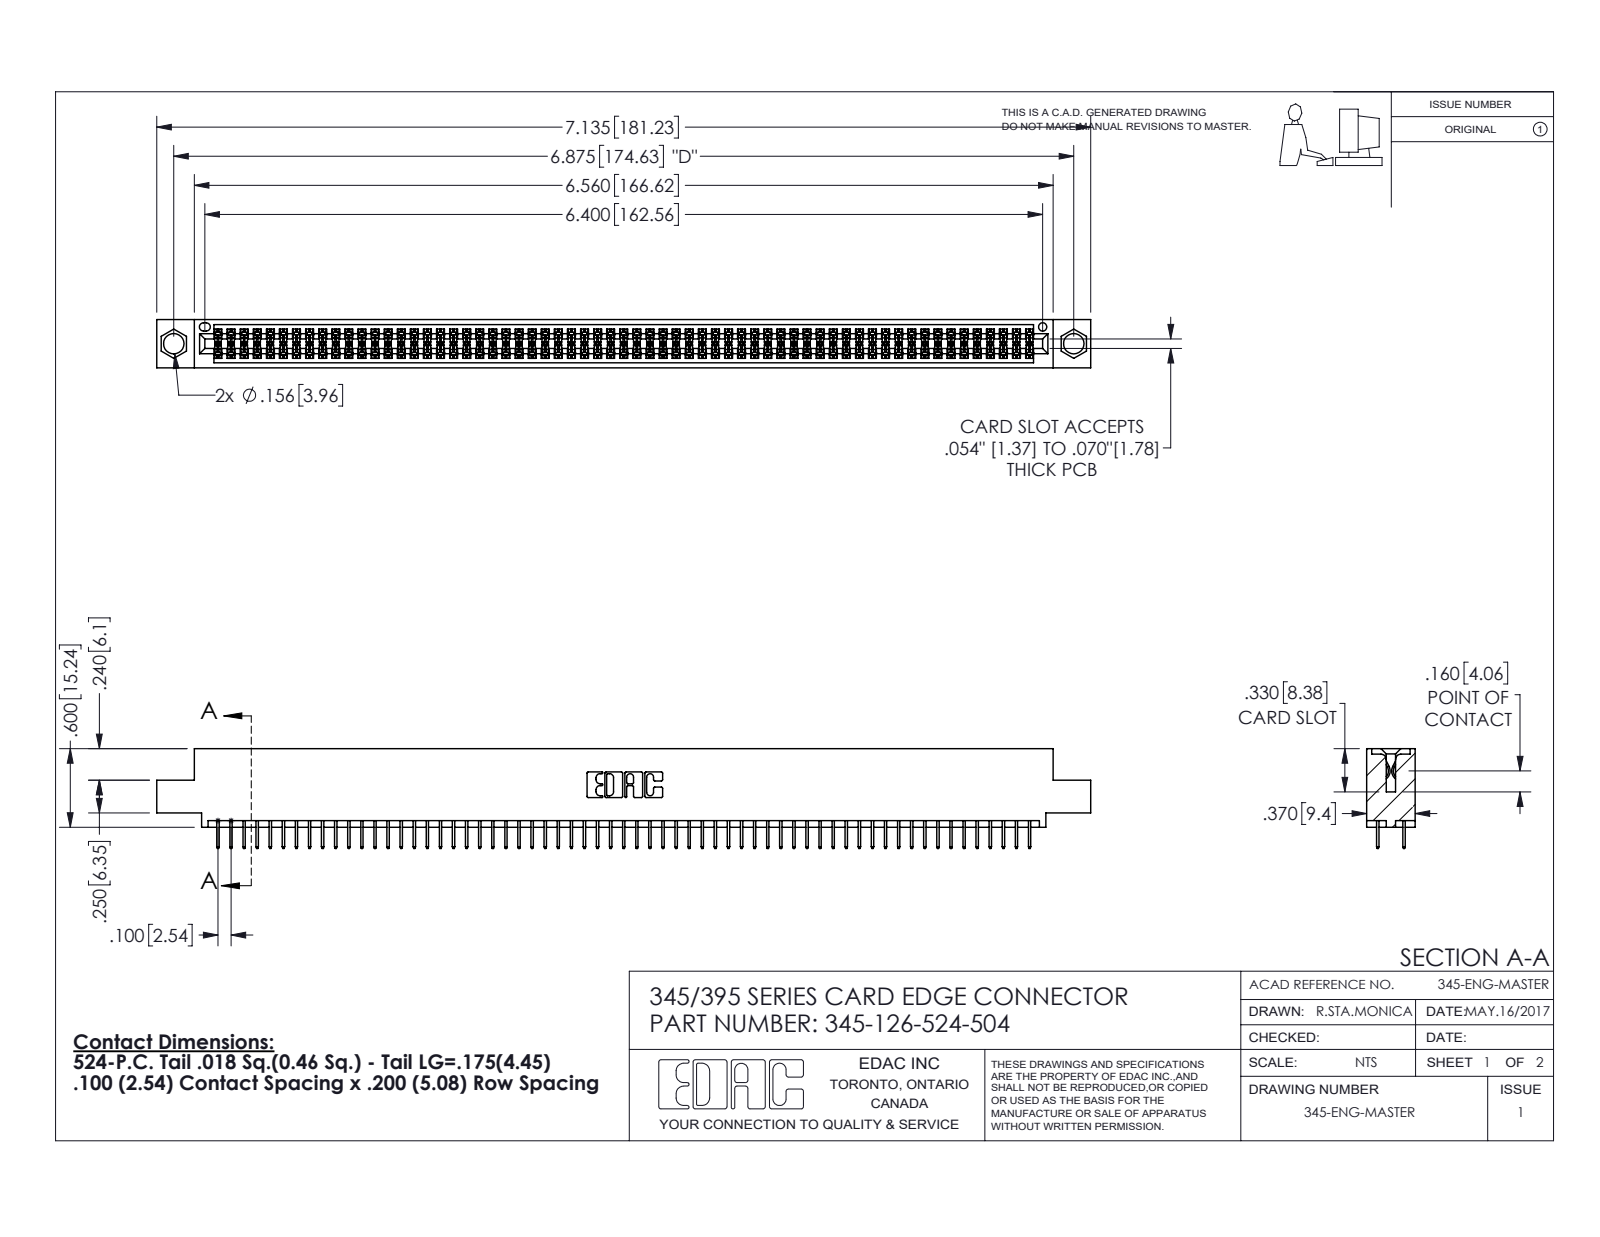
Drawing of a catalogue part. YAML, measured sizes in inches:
part_name: "345-292-001_345-293-124; 345 Part_0.110 Offset - 0.156 Dia-TI; 345-126-524-504"
step_written_by: "SolidWorks 2020 (CONFIG_CONTROL_DESIGN)"
units: inches
bodies: {solids: 127, faces: 6948, planar: 5012, cylindrical: 1936, other: 0}
overall_size: [7.135, 0.762, 0.37]
volume: 1.064
surface_area: 39.7
round_holes:
  - {diameter: 0.156, count: 2}
  - {diameter: 0.064, count: 1}
partial_cylinders:
  - {radius: 0.006, count: 252}
  - {radius: 0.01, count: 22}
  - {radius: 0.007, count: 6}
  - {radius: 0.031, count: 6}
  - {radius: 0.026, count: 3}
  - {radius: 0.014, count: 2}
  - {radius: 0.019, count: 2}
  - {radius: 0.022, count: 2}
face_to_face_distances: [0.072, 0.298, 0.2, 0.37, 0.098, 0.272, 0.025, 0.225, 0.072, 0.175]
hole_center_spacings: [0.27, 6.639, 6.875]
